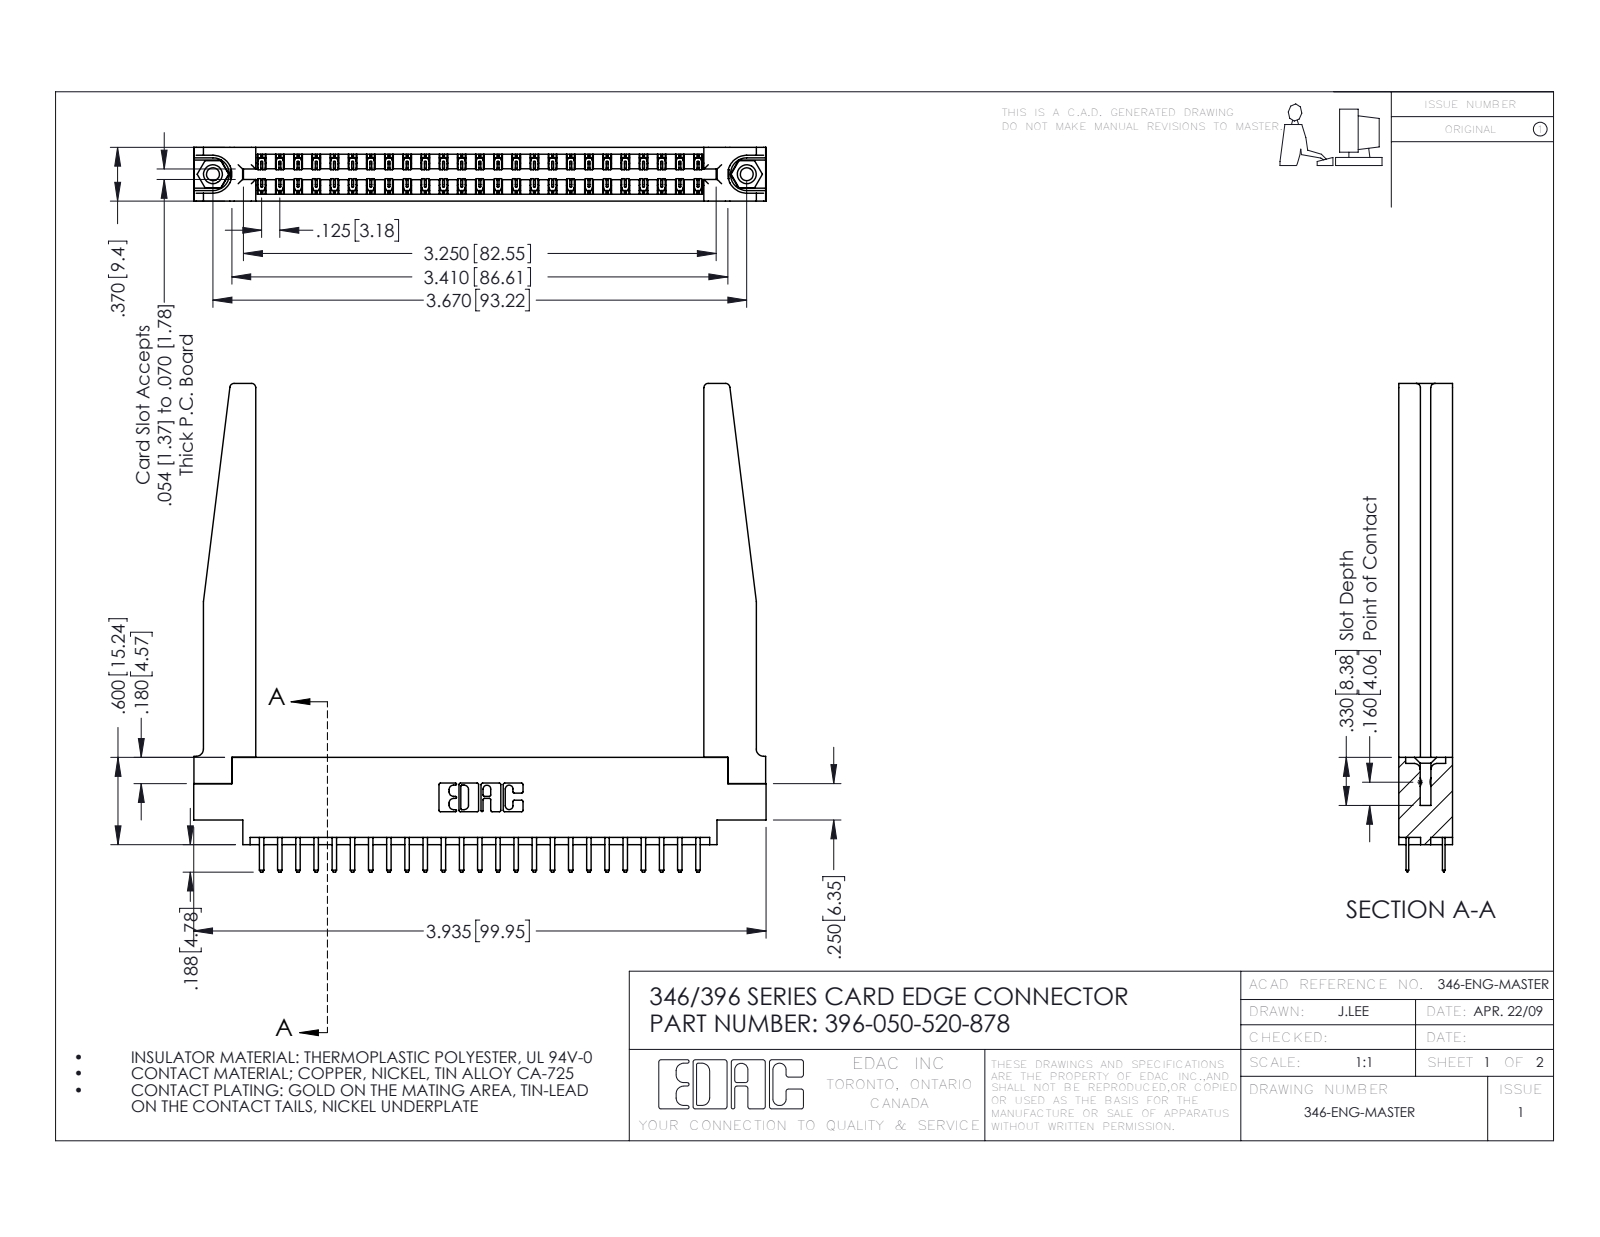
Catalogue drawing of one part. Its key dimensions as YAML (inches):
part_name: "346-220-078_345-220-078; 396-050-520-878; 345-292-001_345-293-120; 345-250-001_345-250-001-102 (+1 more)"
step_written_by: "SolidWorks 2016 (CONFIG_CONTROL_DESIGN)"
units: inches
bodies: {solids: 55, faces: 3160, planar: 2072, cylindrical: 1036, other: 52}
overall_size: [3.935, 3.358, 0.37]
volume: 0.998
surface_area: 30.03
round_holes:
  - {diameter: 0.089, count: 2}
  - {diameter: 0.125, count: 2}
  - {diameter: 0.156, count: 2}
  - {diameter: 0.064, count: 1}
round_bosses_or_shafts:
  - {diameter: 0.155, count: 2}
partial_cylinders:
  - {radius: 0.006, count: 75}
  - {radius: 0.01, count: 54}
  - {radius: 0.01, count: 22}
  - {radius: 0.03, count: 8}
  - {radius: 0.007, count: 6}
  - {radius: 0.031, count: 6}
  - {radius: 0.026, count: 3}
  - {radius: 0.014, count: 2}
face_to_face_distances: [0.37, 0.048, 0.322, 0.072, 0.148, 0.15, 0.25, 0.298, 0.025, 0.275]
hole_center_spacings: [0.246, 3.462, 3.67]
